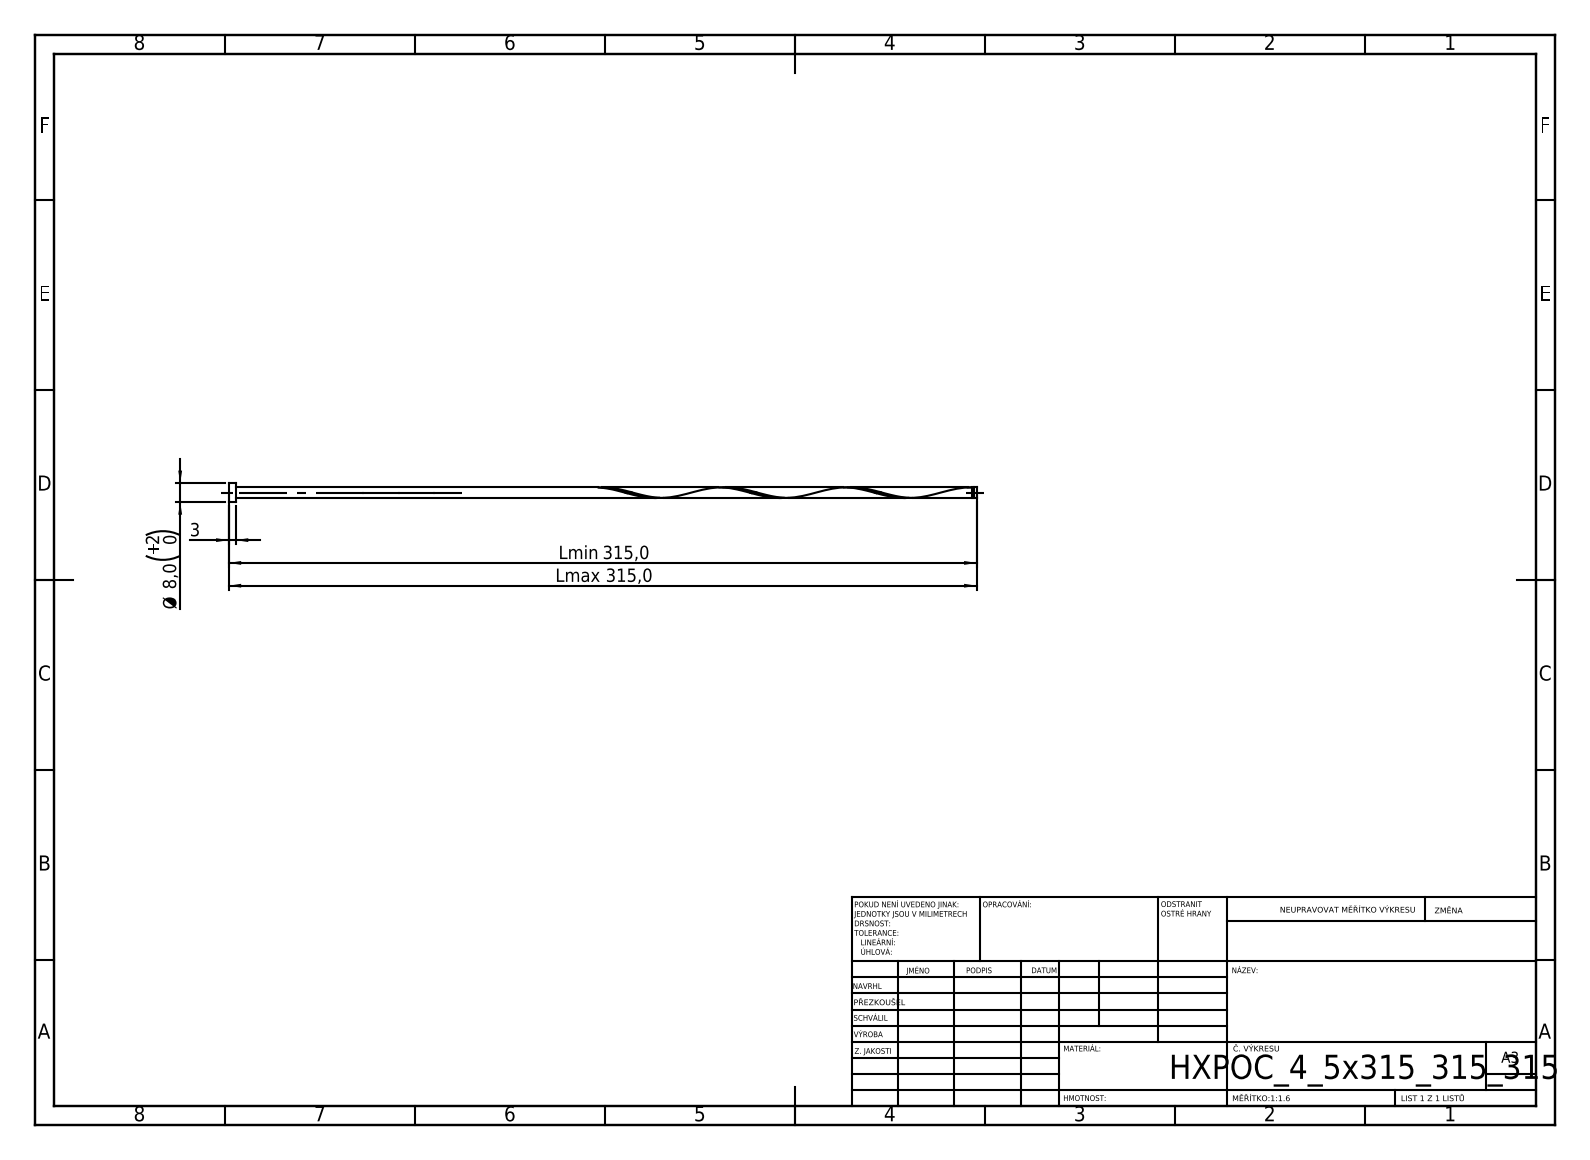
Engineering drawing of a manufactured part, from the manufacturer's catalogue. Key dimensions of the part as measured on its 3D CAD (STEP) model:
STEP written by: SolidWorks 2019 (CONFIG_CONTROL_DESIGN)
Units: millimetres
Bodies: 1 solid, 16 faces (6 planar, 9 cylindrical, 1 other)
Overall size (bounding box): 315 × 8 × 8
Volume: 6 173 mm³ · Surface area: 6 150 mm²
Round bosses / shafts (diameter × count): ⌀8 ×1, ⌀4.5 ×1, ⌀3.6 ×1
Main face-to-face distances: 3, 315, 312, 313.83, 310.83, 1.17, 312.93, 309.93, 0.9, 2.07
